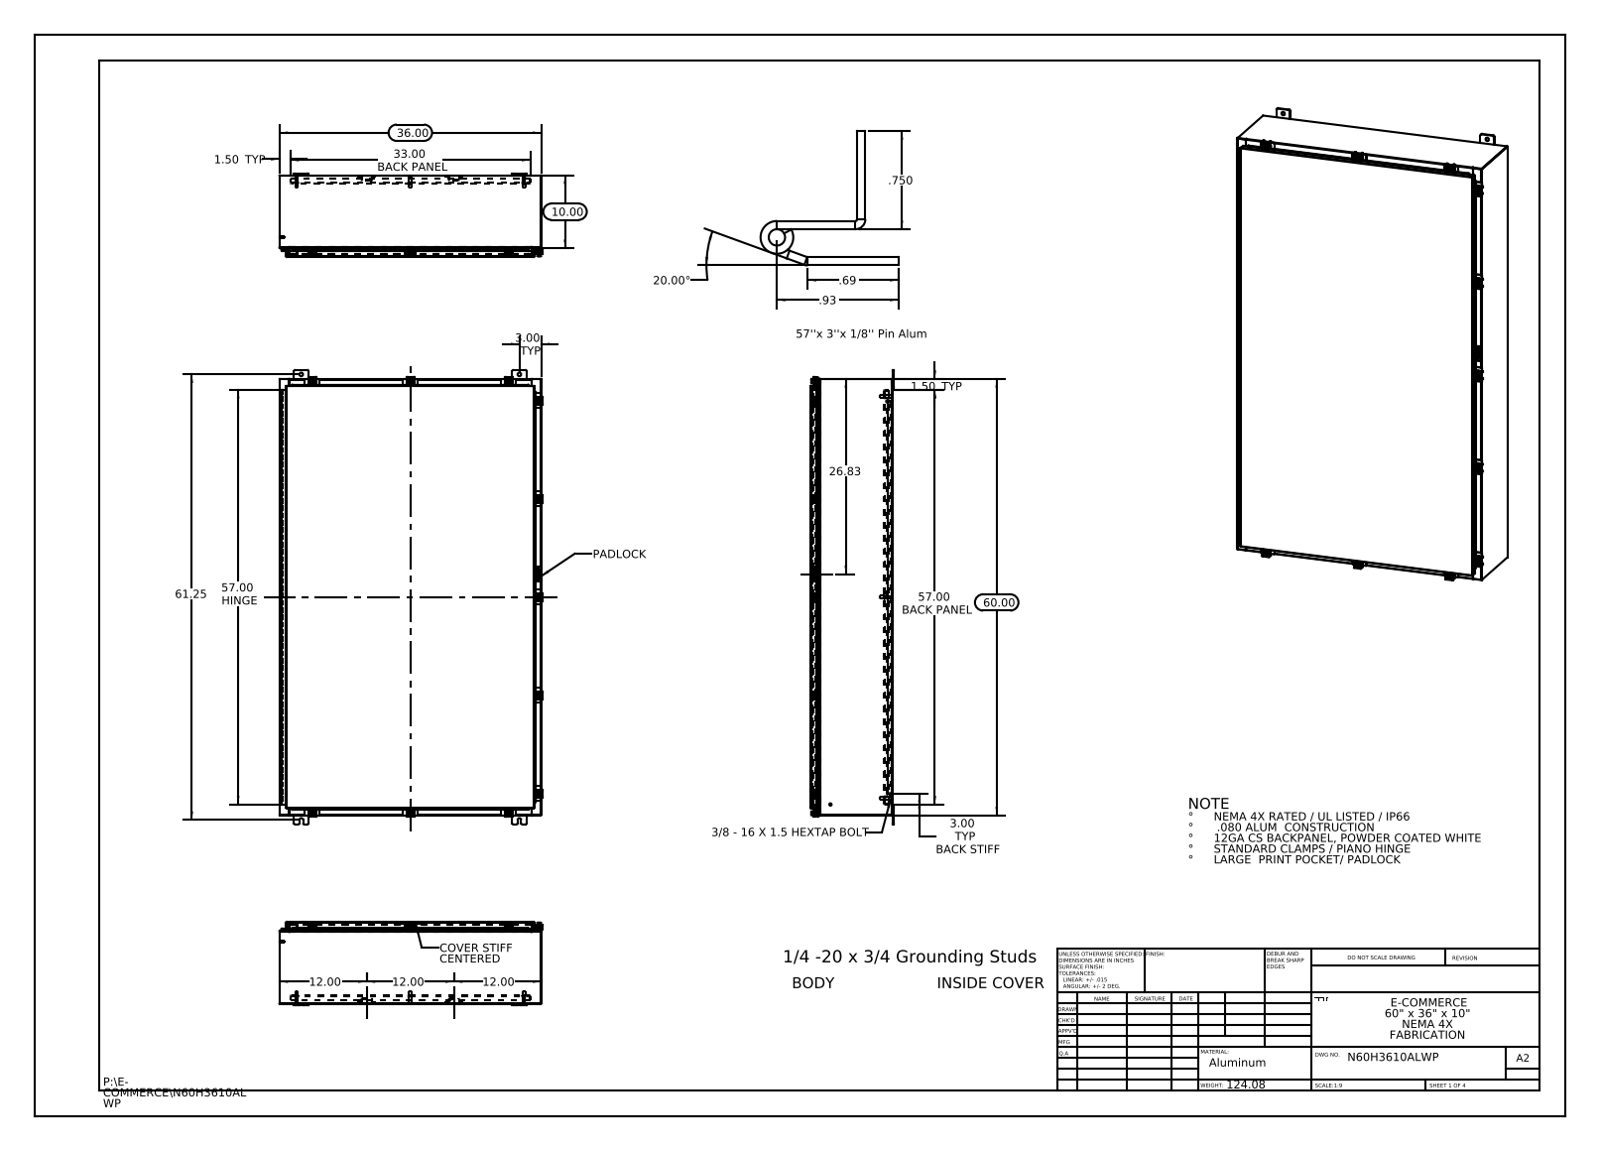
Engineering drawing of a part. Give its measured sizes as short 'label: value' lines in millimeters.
name: 10_30 CD Stud; N60H3610ALWP; N60H3610ALWP Enclosure Stiffener; N60H3610ALWP Hinge Cover Side (+8 more)
written by: SolidWorks 2013 (CONFIG_CONTROL_DESIGN)
unit: mm
bodies: 89 solids, 3554 faces (1796 planar, 1506 cylindrical, 252 other)
size: 1587.5 × 919.8 × 289.3
volume: 12 580 000 mm³; area: 12 310 000 mm²
holes: 12× ⌀12.7, 11× ⌀5.4, 11× ⌀6.6, 8× ⌀6.4, 2× ⌀3.2, 1× ⌀3.2
bosses: 12× ⌀6.4, 11× ⌀12.7, 11× ⌀10.1, 8× ⌀15.9, 8× ⌀9.5, 8× ⌀8.4, 8× ⌀4, 8× ⌀3.6
rounds: 50× R1.5, 39× R0.3, 33× R2.2, 24× R4.8, 22× R3, 22× R3.6, 17× R1.3, 16× R2
face distances: 1.9, 282.6, 280.7, 2.6, 284.5, 25.4, 257.2, 27.3, 255.3, 29.9
hole spacings: 342.9, 347, 56.5, 685.8, 701.7, 757, 1059.4, 1457.7
